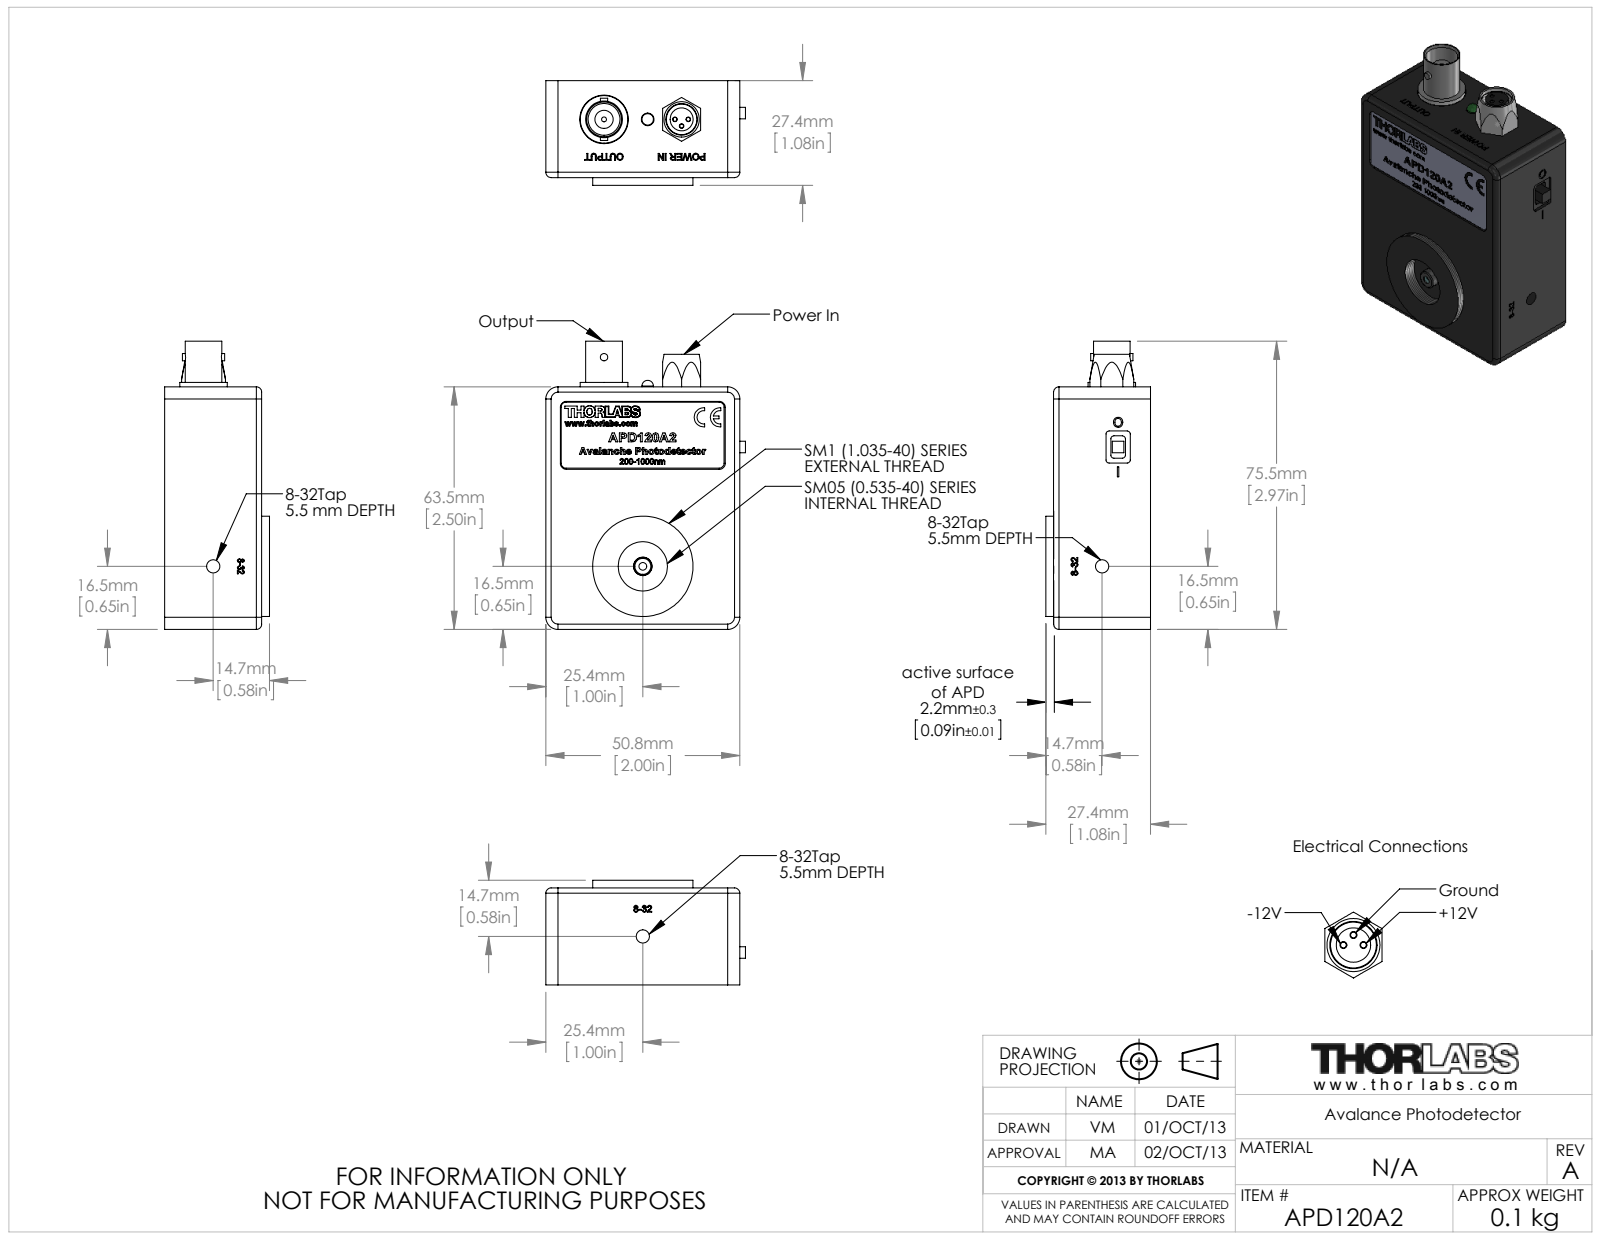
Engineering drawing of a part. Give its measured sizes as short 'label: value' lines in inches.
name: APD110A2-Baugruppe; APD120x-Folie_APD120A2; countersunk flat head cross recess screw_din_ISO 7046-1 - M2 x 4 - Z --- 4N; M0092-0545-0A-Deckel (+7 more)
written by: SolidWorks 2012 (CONFIG_CONTROL_DESIGN)
unit: in
bodies: 75 solids, 2335 faces (1392 planar, 283 cylindrical, 660 other)
size: 2.971 × 2.057 × 1.08
volume: 2.412 in³; area: 52.36 in²
holes: 8× ⌀0.063, 4× ⌀0.094, 4× ⌀0.096, 3× ⌀0.018, 3× ⌀0.039, 3× ⌀0.04, 2× ⌀0.136, 1× ⌀0.05, 1× ⌀0.052, 1× ⌀0.079, 1× ⌀0.098, 1× ⌀0.13
bosses: 6× ⌀0.02, 5× ⌀0.15, 4× ⌀0.079, 3× ⌀0.018, 1× ⌀1.035, 1× ⌀0.49, 1× ⌀0.43, 1× ⌀0.378
rounds: 18× R0.125, 14× R0.13, 10× R0.031, 8× R0.031, 8× R0.075, 8× R0.095, 4× R0.05, 4× R0.055
face distances: 0.063, 0.452, 0.515, 0.1, 0.389, 0.063, 0.452, 1, 0.937, 0.548
hole spacings: 1.621, 1.55, 0.174, 0.822, 0.841, 2.013, 2.579, 0.05
